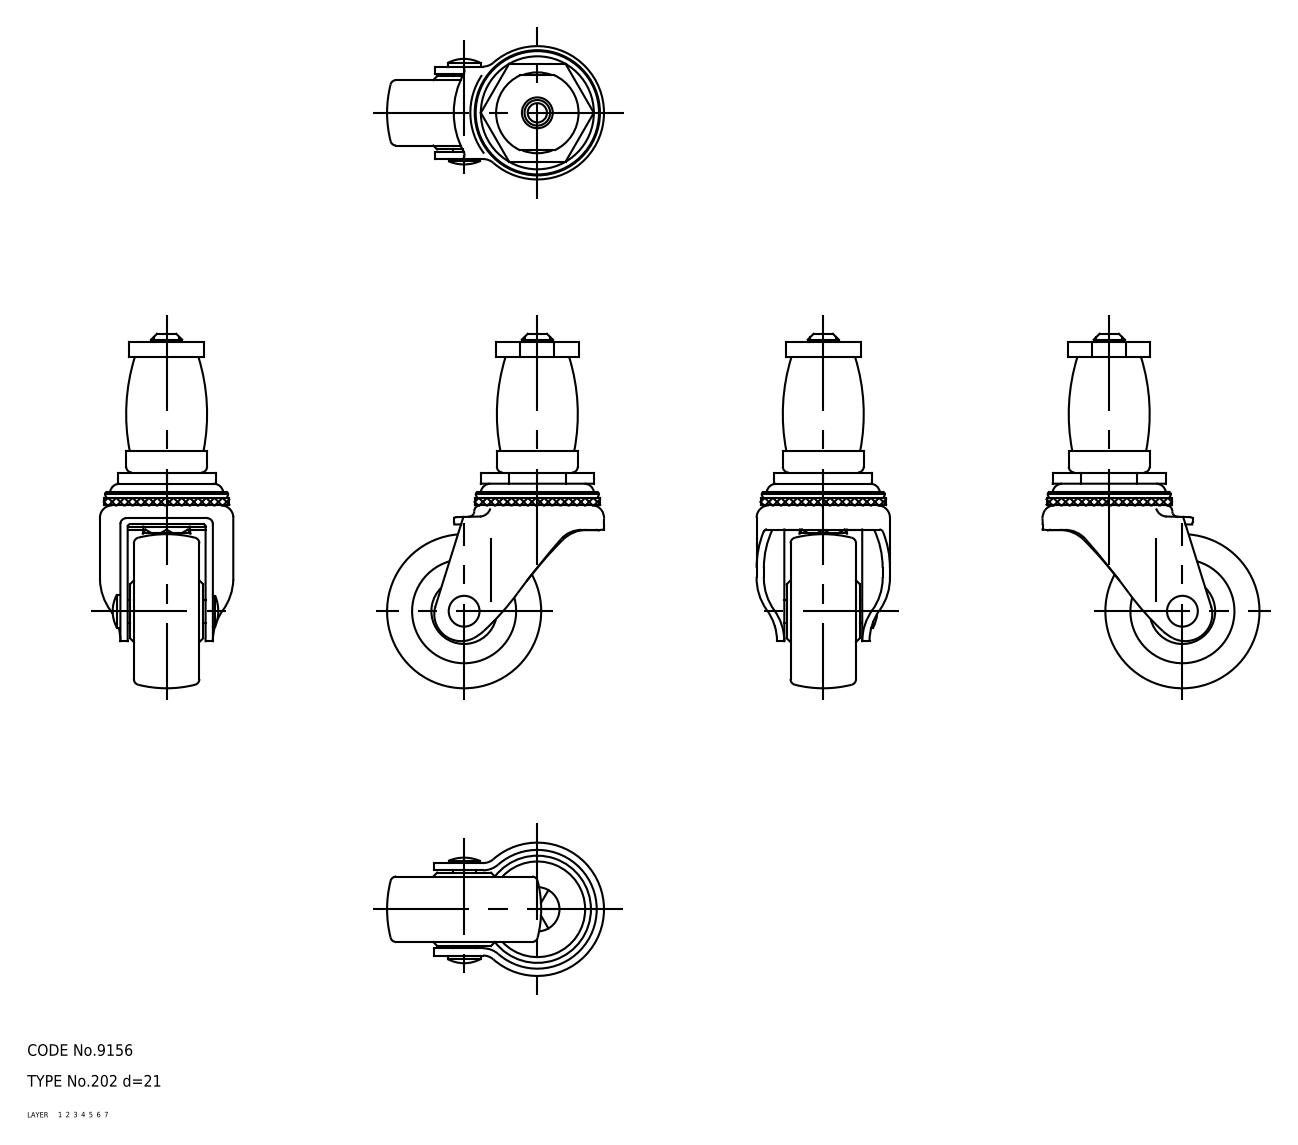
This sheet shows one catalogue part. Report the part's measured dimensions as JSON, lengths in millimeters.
{"part_name": "wheel; main shaft; axle; No_202_d21_21167_36", "step_written_by": "CADfix (AUTOMOTIVE_DESIGN)", "units": "millimeters", "bodies": {"solids": 4, "faces": 182, "planar": 0, "cylindrical": 0, "other": 182}, "overall_size": [92, 56.3, 34.6], "volume_mm3": 40240, "surface_area_mm2": 17178}
